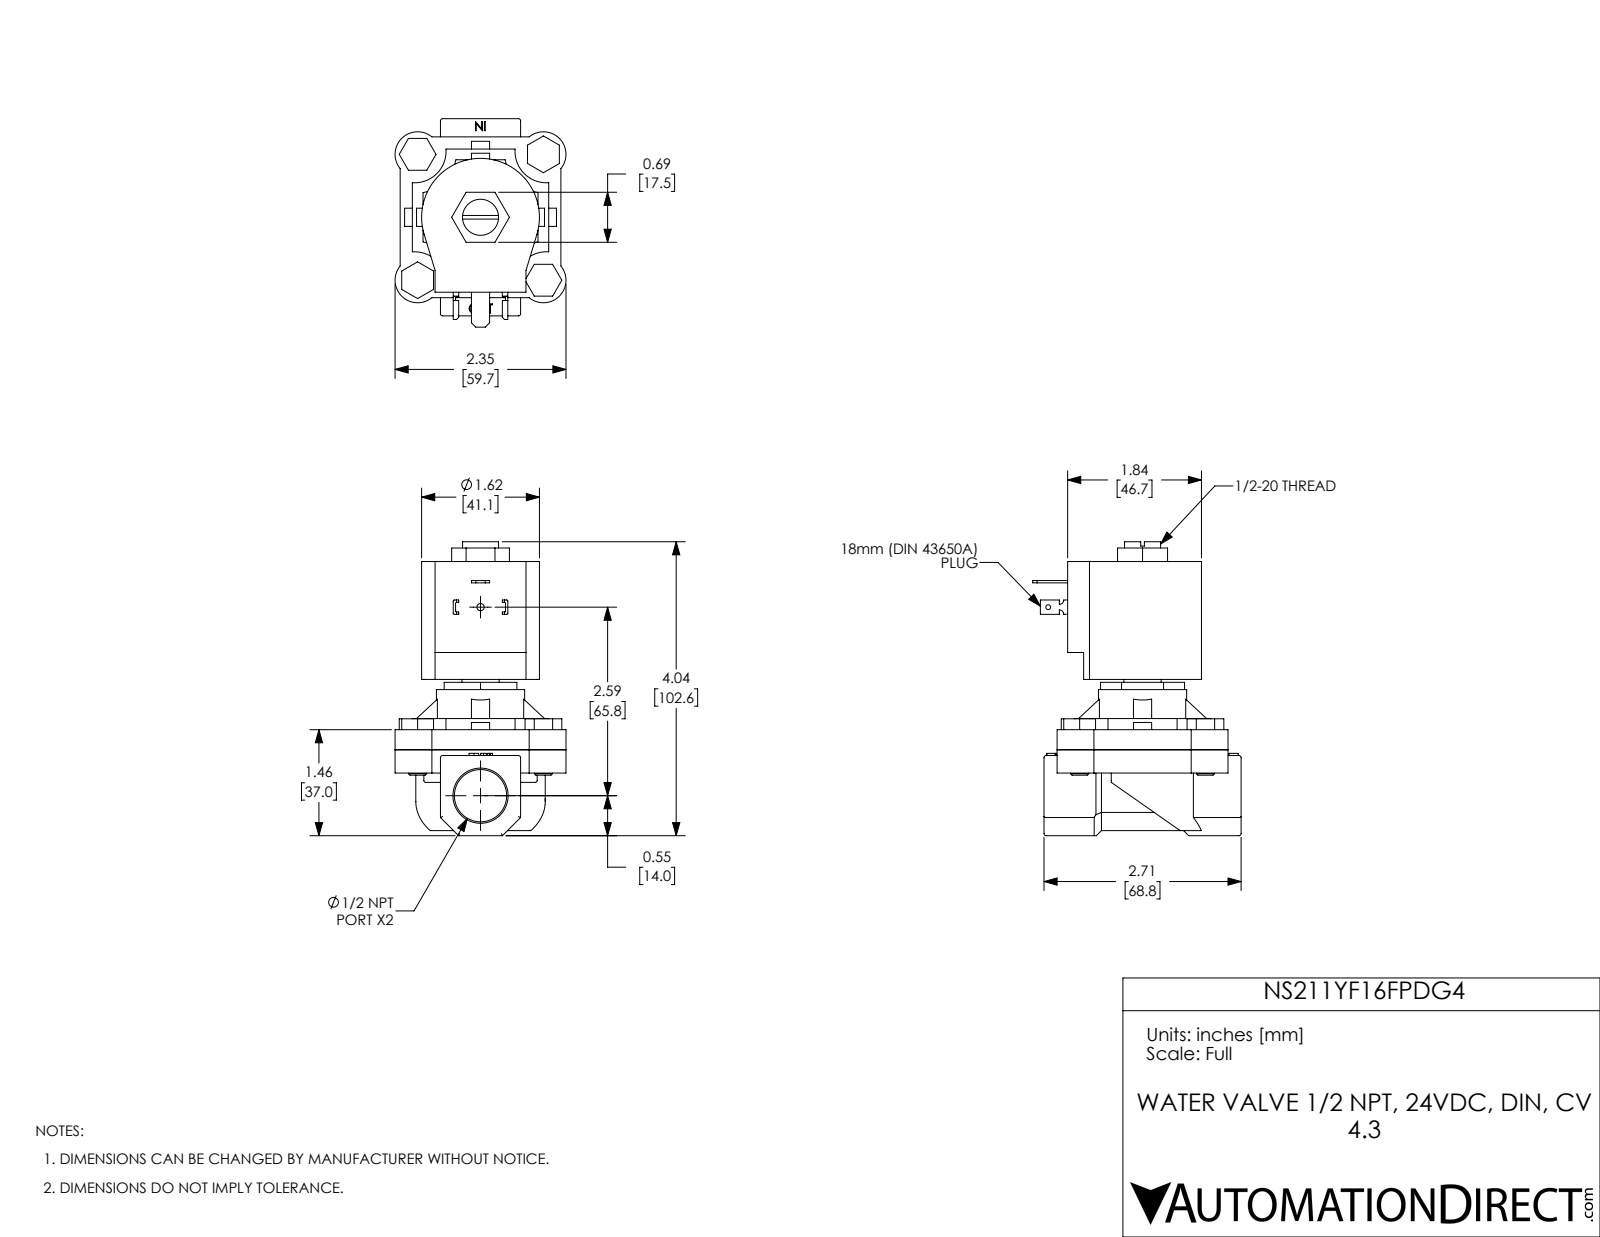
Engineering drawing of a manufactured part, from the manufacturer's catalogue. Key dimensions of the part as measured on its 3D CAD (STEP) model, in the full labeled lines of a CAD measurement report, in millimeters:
Part name (STEP PRODUCT): NS211YF16FPDG4
STEP written by: SolidWorks 2017 (AUTOMOTIVE_DESIGN)
Units: millimetres
Bodies: 11 solids, 385 faces (239 planar, 113 cylindrical, 33 other)
Overall size (bounding box): 102.6 × 72.8 × 59.7
Volume: 165 500 mm³ · Surface area: 43 680 mm²
Round holes (diameter × count): ⌀6.4 ×4, ⌀1.7 ×1, ⌀2.5 ×1, ⌀12.6 ×1, ⌀13 ×1, ⌀18.3 ×1, ⌀29.3 ×1
Round bosses / shafts (diameter × count): ⌀6.3 ×4, ⌀30.8 ×1
Partial cylindrical surfaces — rounded edges, fillets, slot ends (radius × count): R0.8 ×15, R0.4 ×8, R7.9 ×4, R11 ×4, R14.7 ×4, R1.5 ×2, R20.6 ×1, R22.6 ×1
Main face-to-face distances: 7, 65.7, 58.7, 8.1, 15.1, 73.8, 14.1, 42.1, 6.4, 56.1
Hole centre spacings: 31.1, 43.9, 62.1, 65.8
